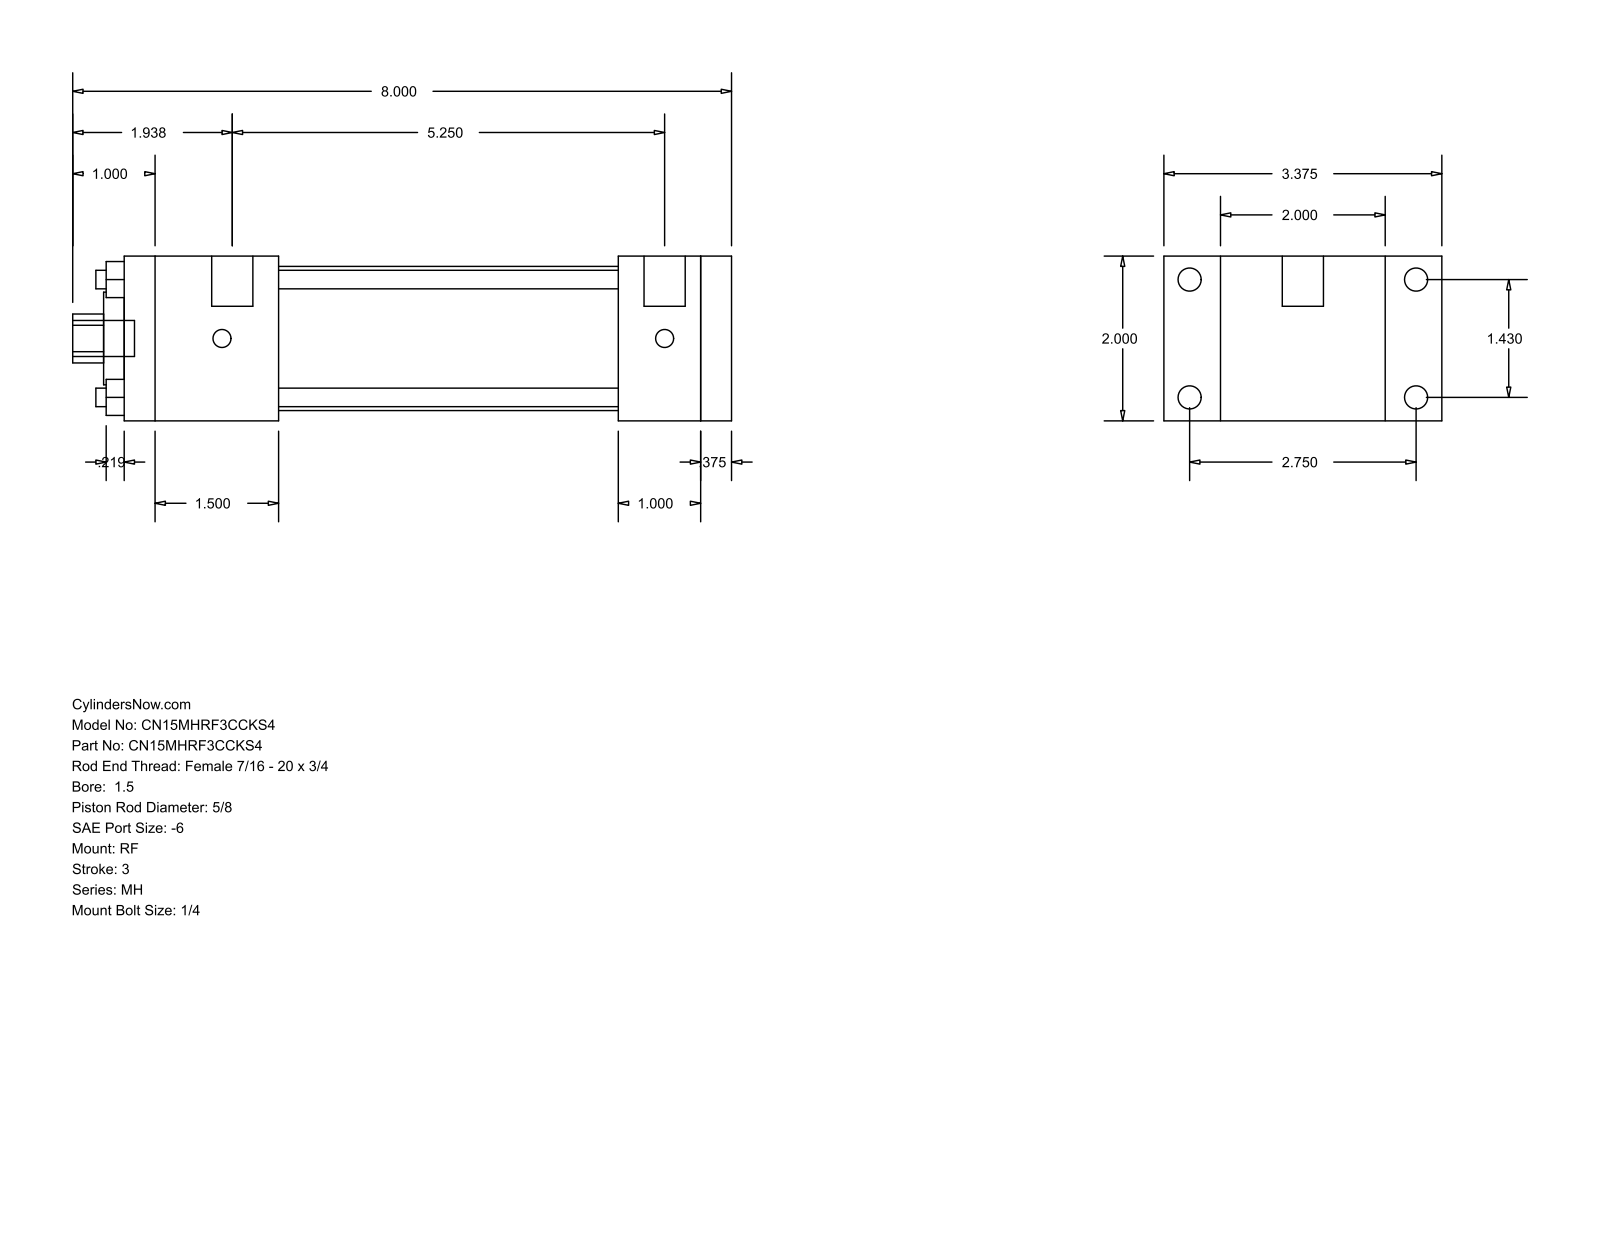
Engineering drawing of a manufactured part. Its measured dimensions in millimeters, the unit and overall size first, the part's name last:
Units: millimetres
Overall size (bounding box): 203.2 × 85.72 × 50.8
Round holes (diameter × count): ⌀5.71 ×4, ⌀15.88 ×1, ⌀28.57 ×1, ⌀44.45 ×1
Round bosses / shafts (diameter × count): ⌀7.14 ×4, ⌀5.56 ×4, ⌀12.7 ×2, ⌀11.11 ×1
Partial cylindrical surfaces — rounded edges, fillets, slot ends (radius × count): R7.54 ×1
Main face-to-face distances: 50.8, 9.52, 177.8, 187.32, 17.46, 68.26, 152.4, 25.4, 34.92, 47.62
Hole centre spacings: 25.68, 36.32, 51.36
Bodies: 0 solids, 92 faces (64 planar, 28 cylindrical, 0 other)
Part name (STEP PRODUCT): MH_RF__0150_0.625
STEP written by: GSSL Pune (CONFIG_CONTROL_DESIGN)
